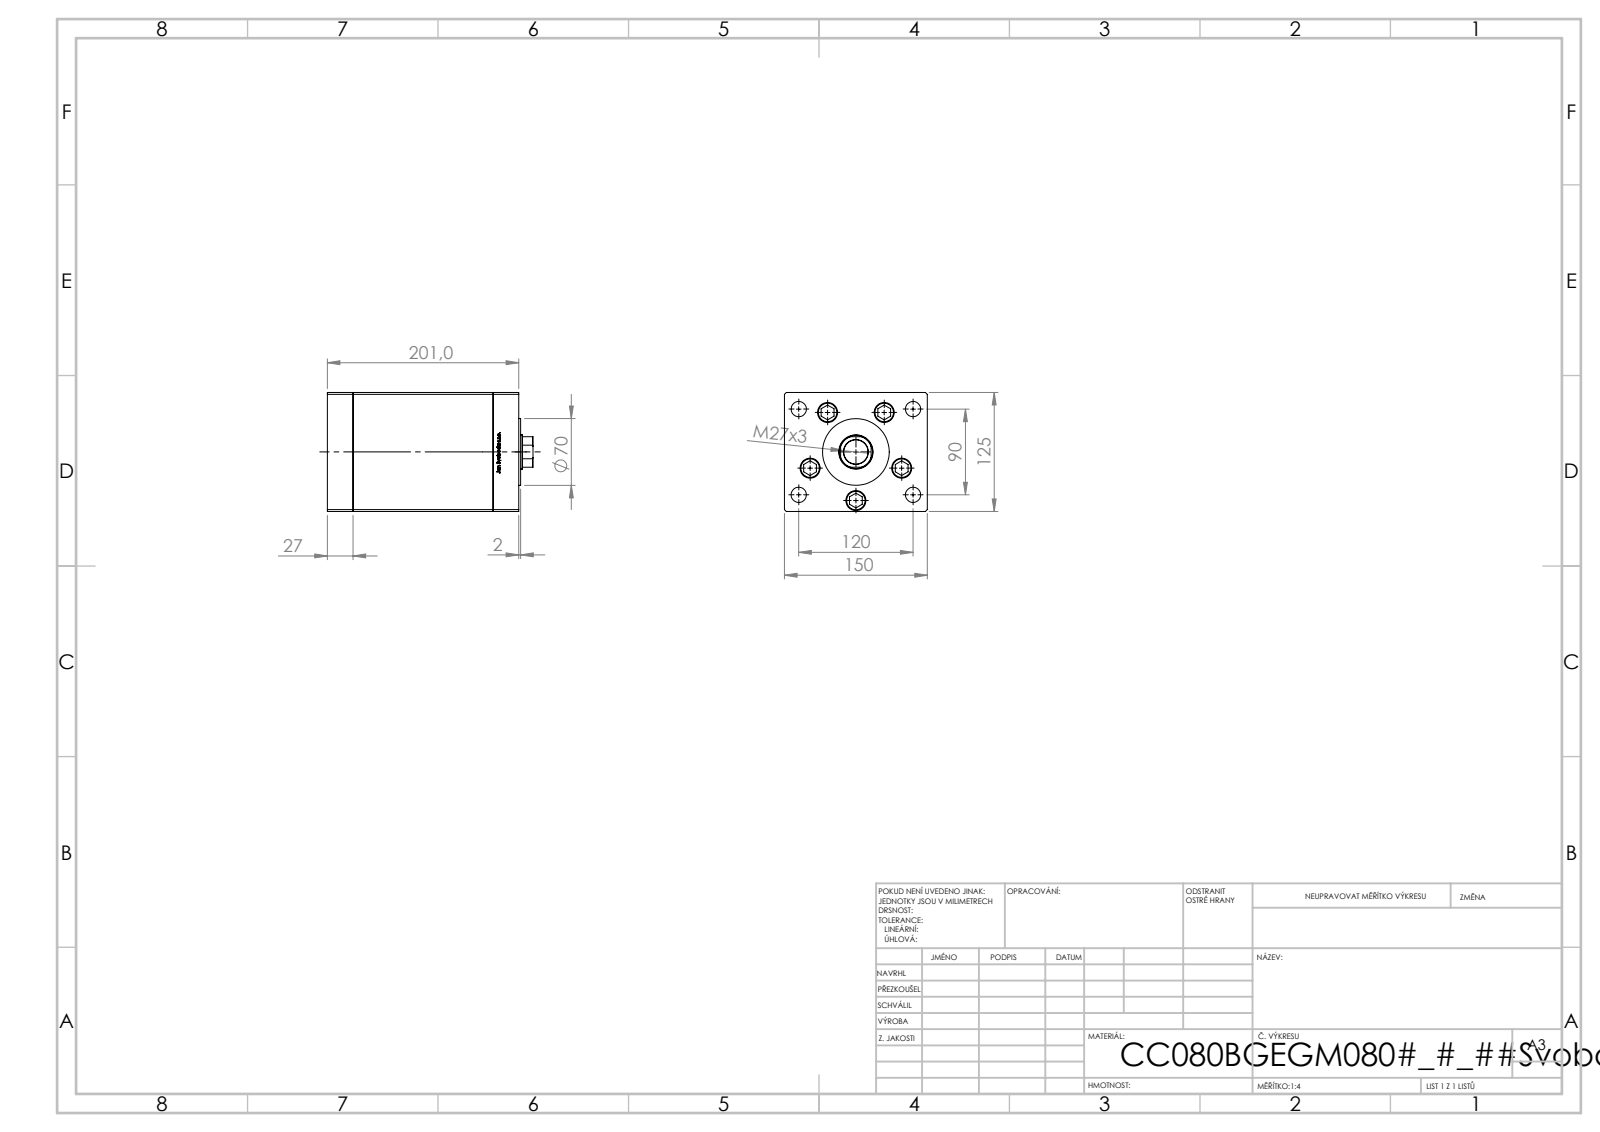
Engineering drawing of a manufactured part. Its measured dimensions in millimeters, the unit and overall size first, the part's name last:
Units: millimetres
Overall size (bounding box): 216 × 150 × 125
Round holes (diameter × count): ⌀17.5 ×5, ⌀21 ×5, ⌀16 ×4, ⌀2 ×2, ⌀13.16 ×2, ⌀25.5 ×1, ⌀36 ×1
Round bosses / shafts (diameter × count): ⌀8 ×5, ⌀80 ×1, ⌀70 ×1
Partial cylindrical surfaces — rounded edges, fillets, slot ends (radius × count): R0.93 ×2, R17.5 ×1
Main face-to-face distances: 27, 174, 147, 125, 150, 33.5, 201, 6.5, 140.5, 167.5
Hole centre spacings: 51, 75, 30.43, 30.48, 58.89, 60.3, 61.25, 63.14
Volume: 3 289 000 mm³ · Surface area: 349 130 mm²
Bodies: 14 solids, 1185 faces (464 planar, 147 cylindrical, 574 other)
Part name (STEP PRODUCT): ALLEN BOLT; V220C BACK_B; V220C_B MIDDLE; V220C_FRONT_B (+1 more)
STEP written by: SolidWorks 2019 (CONFIG_CONTROL_DESIGN)
